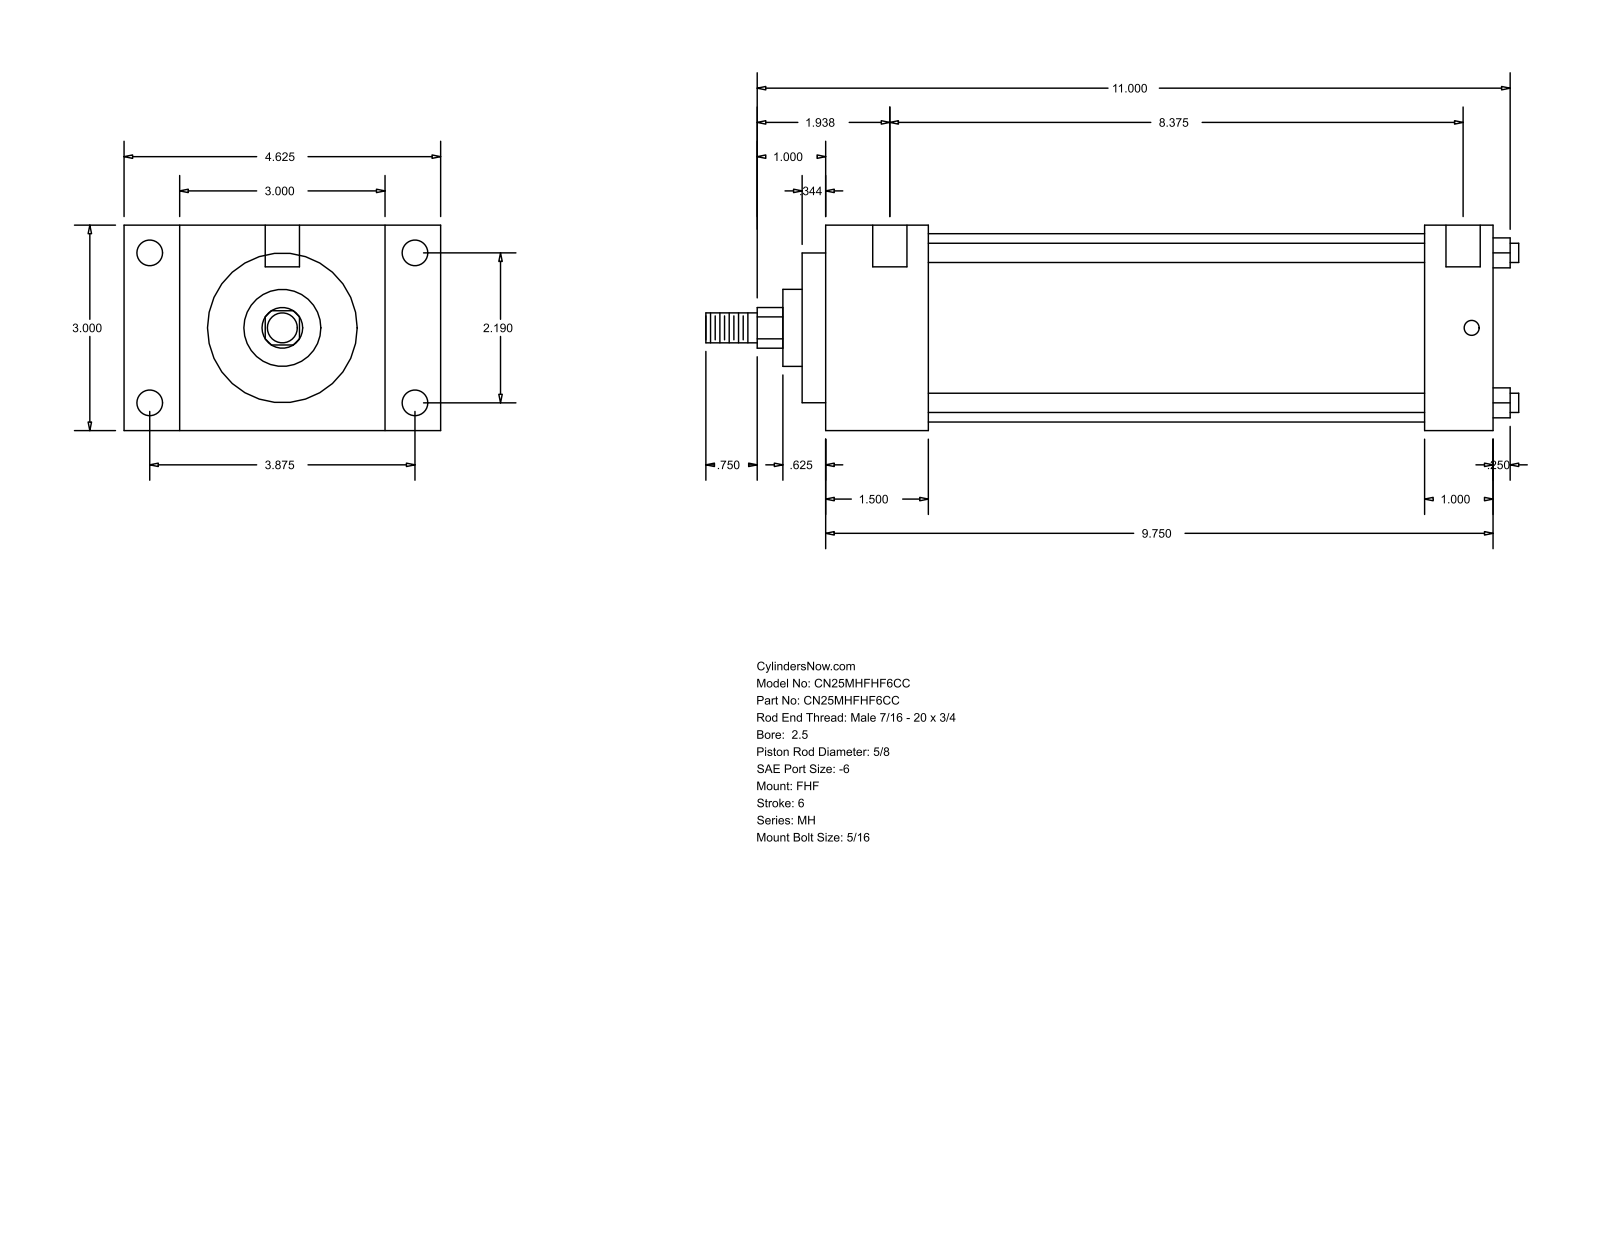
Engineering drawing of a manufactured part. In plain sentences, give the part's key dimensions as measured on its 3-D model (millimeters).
The part is named "MH_FHF__0250_0.625". Its 3-D file was written by "GSSL Pune (CONFIG_CONTROL_DESIGN)". It is 0 solids with 90 faces: 61 planar, 29 cylindrical and 0 other. Overall it measures 301.62 by 117.47 by 76.2 millimeters. Round holes: 4 of diameter 5.56, 4 of diameter 9.53, 2 of diameter 12.7. Round bosses or shafts: 4 of diameter 7.14, 1 of diameter 69.85, 1 of diameter 55.55, 1 of diameter 28.57, 1 of diameter 15.88, 1 of diameter 11.11. Partial cylindrical surfaces (rounded edges, fillets, slot ends): 1 of radius 7.54. The main face-to-face distances are 76.2, 247.65, 38.1, 209.55, 20.64, 96.84, 117.48, 25.4, 222.25, 184.15. The hole center spacings are 55.62, 98.42, 113.05, 220.66, 3.17, 4.76, 212.73, 215.9.
